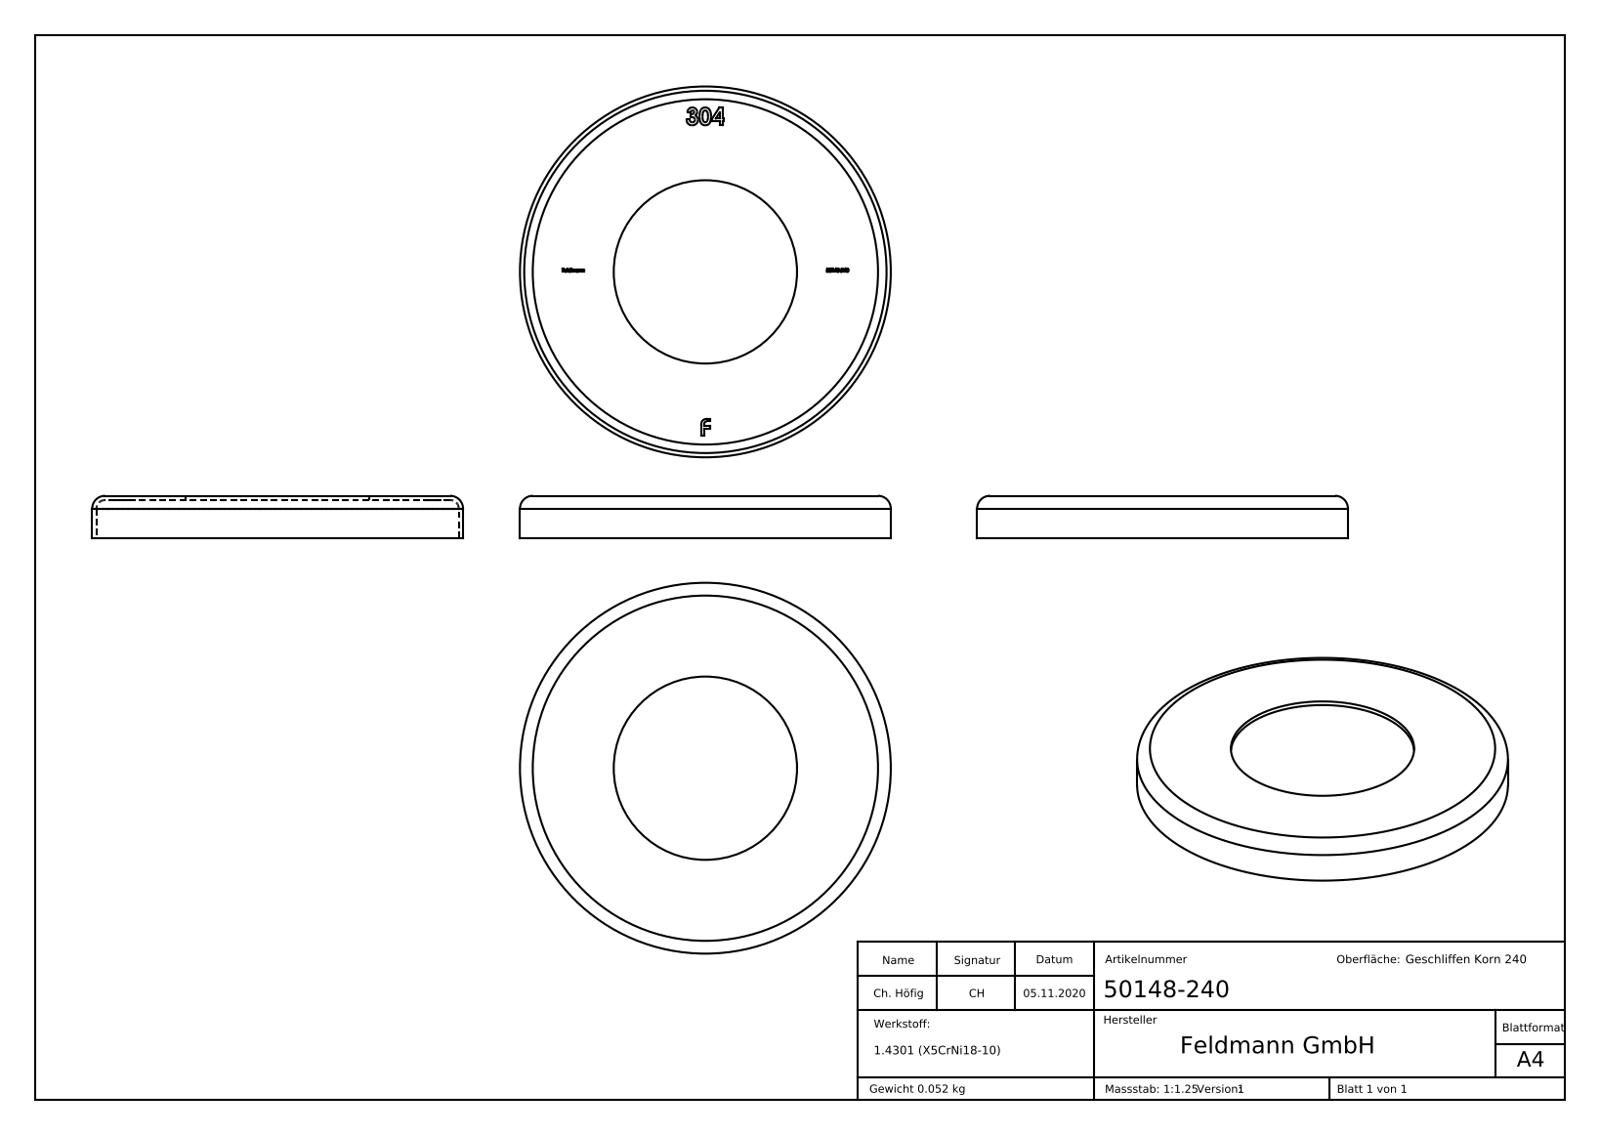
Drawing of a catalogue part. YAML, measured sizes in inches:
part_name: "50148-240"
step_written_by: "SolidWorks 2018 (CONFIG_CONTROL_DESIGN)"
units: inches
bodies: {solids: 1, faces: 296, planar: 164, cylindrical: 6, other: 126}
overall_size: [3.425, 3.425, 0.394]
volume: 0.405
surface_area: 21.21
round_holes:
  - {diameter: 1.693, count: 1}
  - {diameter: 3.346, count: 1}
round_bosses_or_shafts:
  - {diameter: 3.425, count: 1}
face_to_face_distances: [0.039, 0.354, 0.394, 0.358, 0.035, 0.028, 0.197, 0.169, 0.023, 0.027]
